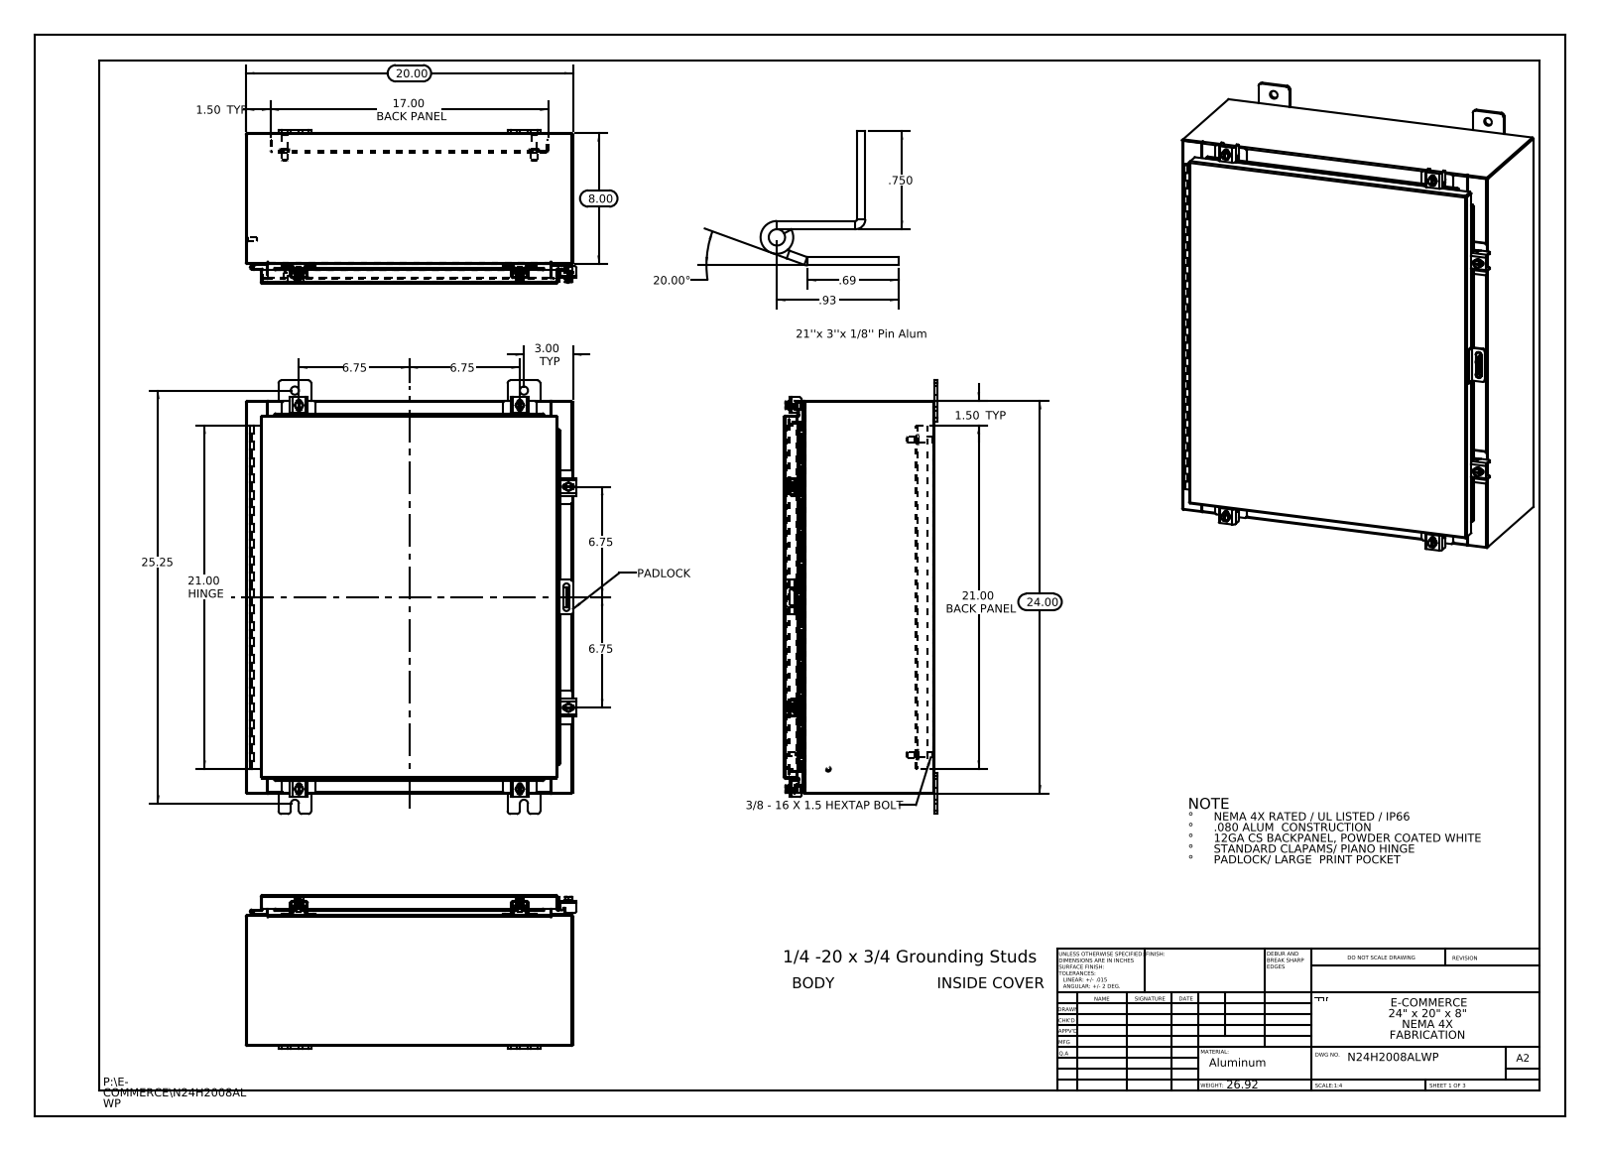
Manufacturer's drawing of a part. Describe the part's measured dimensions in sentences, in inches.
The part is named "N24H2008ALWP Padlock Staple; N24H2008ALWP 22101002; N24H2008ALWP Hinge Enclosure Side2; N24H2008ALWP Padlock Hasp (+8 more)". Its 3-D file was written by "SolidWorks 2013 (CONFIG_CONTROL_DESIGN)". It is 49 solids with 1735 faces: 914 planar, 713 cylindrical and 108 other. Overall it measures 26.5 by 20.211 by 9.389 inches. Its volume is 187 cubic inches and its surface area 4 713 square inches. Round holes: 8 of diameter 0.5, 6 of diameter 0.213, 6 of diameter 0.26, 2 of diameter 0.125, 1 of diameter 0.125. Round bosses or shafts: 7 of diameter 0.25, 6 of diameter 0.5, 6 of diameter 0.399, 4 of diameter 0.625, 4 of diameter 0.375, 4 of diameter 0.33, 2 of diameter 0.315, 2 of diameter 0.236. Partial cylindrical surfaces (rounded edges, fillets, slot ends): 30 of radius 0.06, 25 of radius 0.013, 24 of radius 0.19, 21 of radius 0.088, 12 of radius 0.12, 12 of radius 0.141, 10 of radius 0.125, 9 of radius 0.05. The main face-to-face distances are 0.075, 9.126, 9.051, 9.201, 0.104, 19.925, 1, 1.075, 8.051, 8.126. The hole center spacings are 21.369, 25.739, 13.5, 0.431, 0.934, 1.858, 2.275, 2.276.
